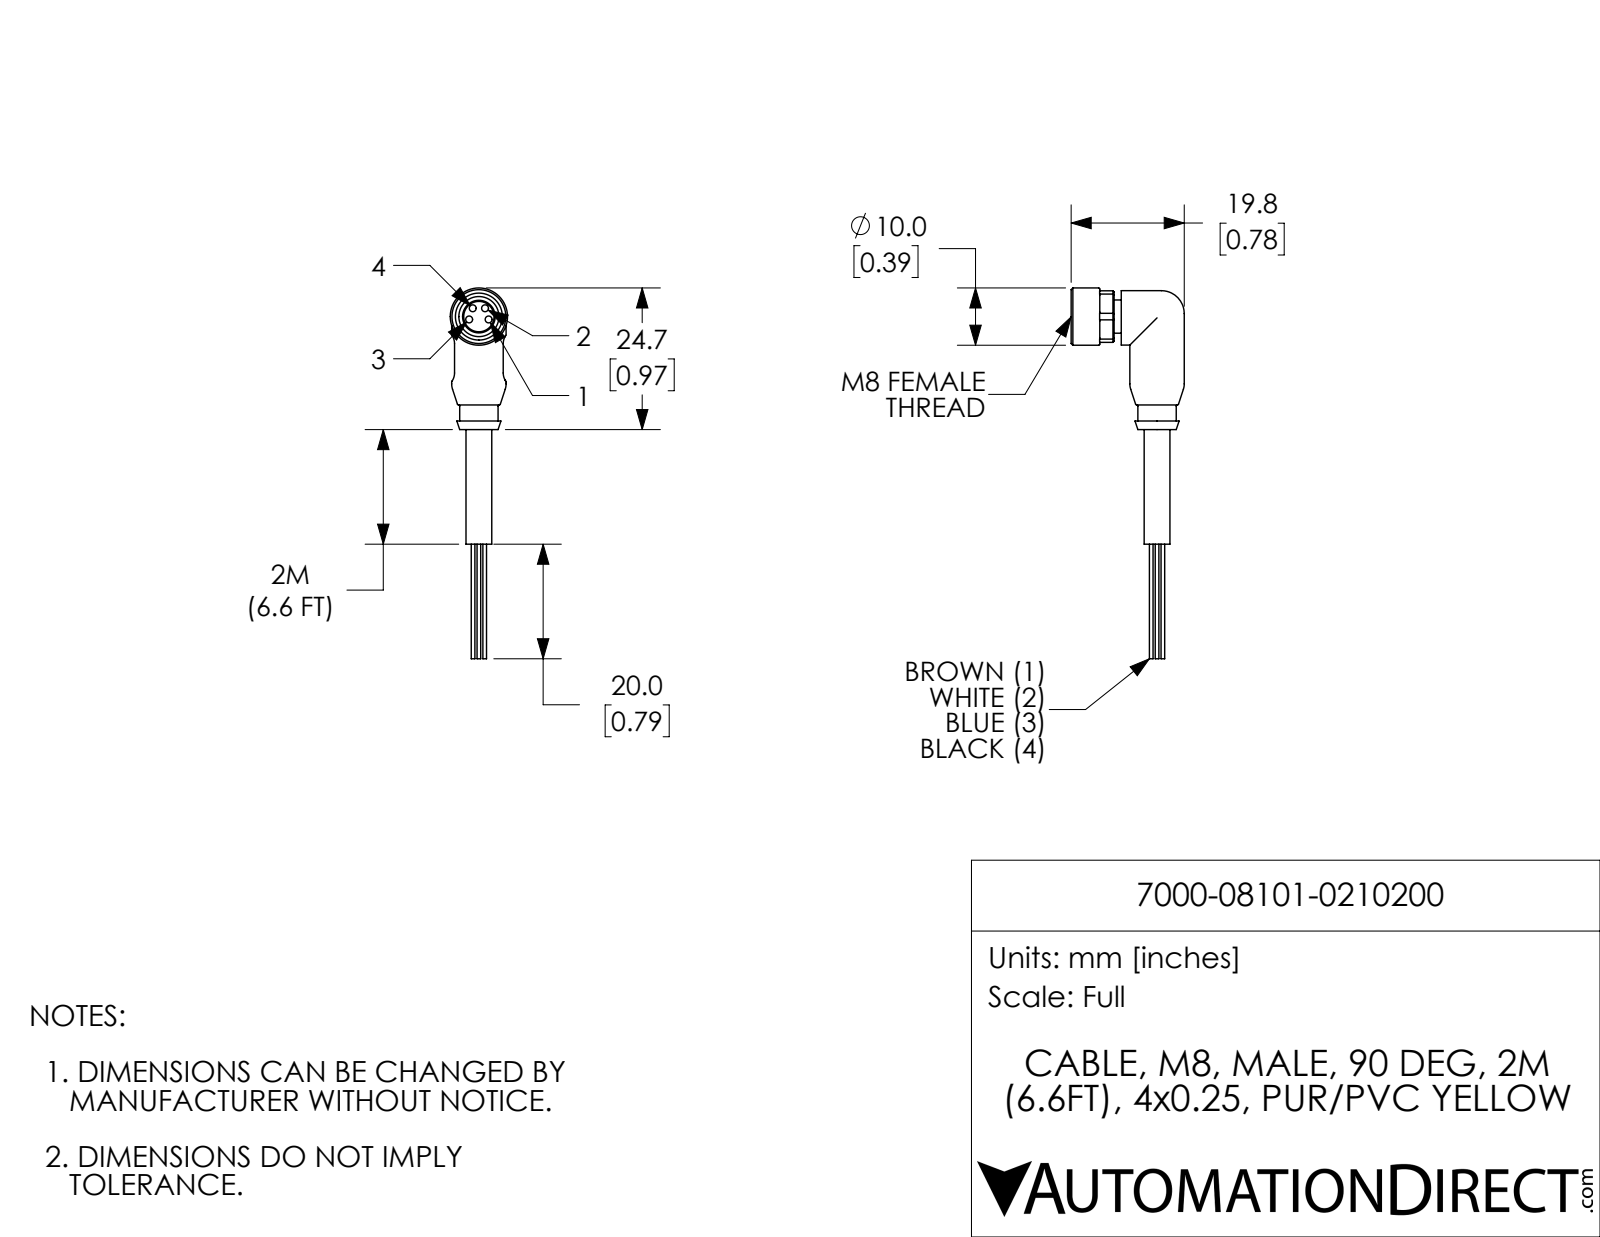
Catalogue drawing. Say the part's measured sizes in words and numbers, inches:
The part is named "7000-08101-0210200". Its 3-D file was written by "SolidWorks 2017 (AUTOMOTIVE_DESIGN)". It is 5 solids with 117 faces: 41 planar, 47 cylindrical and 29 other. Overall it measures 2.548 by 0.778 by 0.394 inches. Its volume is 0.147 cubic inches and its surface area 2.976 square inches. Round holes: 4 of diameter 0.047, 1 of diameter 0.276. Round bosses or shafts: 3 of diameter 0.025, 2 of diameter 0.374, 1 of diameter 0.394, 1 of diameter 0.264, 1 of diameter 0.228, 1 of diameter 0.224, 1 of diameter 0.177, 1 of diameter 0.025. Partial cylindrical surfaces (rounded edges, fillets, slot ends): 4 of radius 0.008, 4 of radius 0.098, 1 of radius 0.193. The main face-to-face distances are 0.049, 0.354, 0.059, 0.335, 0.028, 0.787, 0.268, 0.317, 0.295, 0.344. The hole center spacings are 0.07, 0.071, 0.081, 0.133, 0.084, 0.134.
